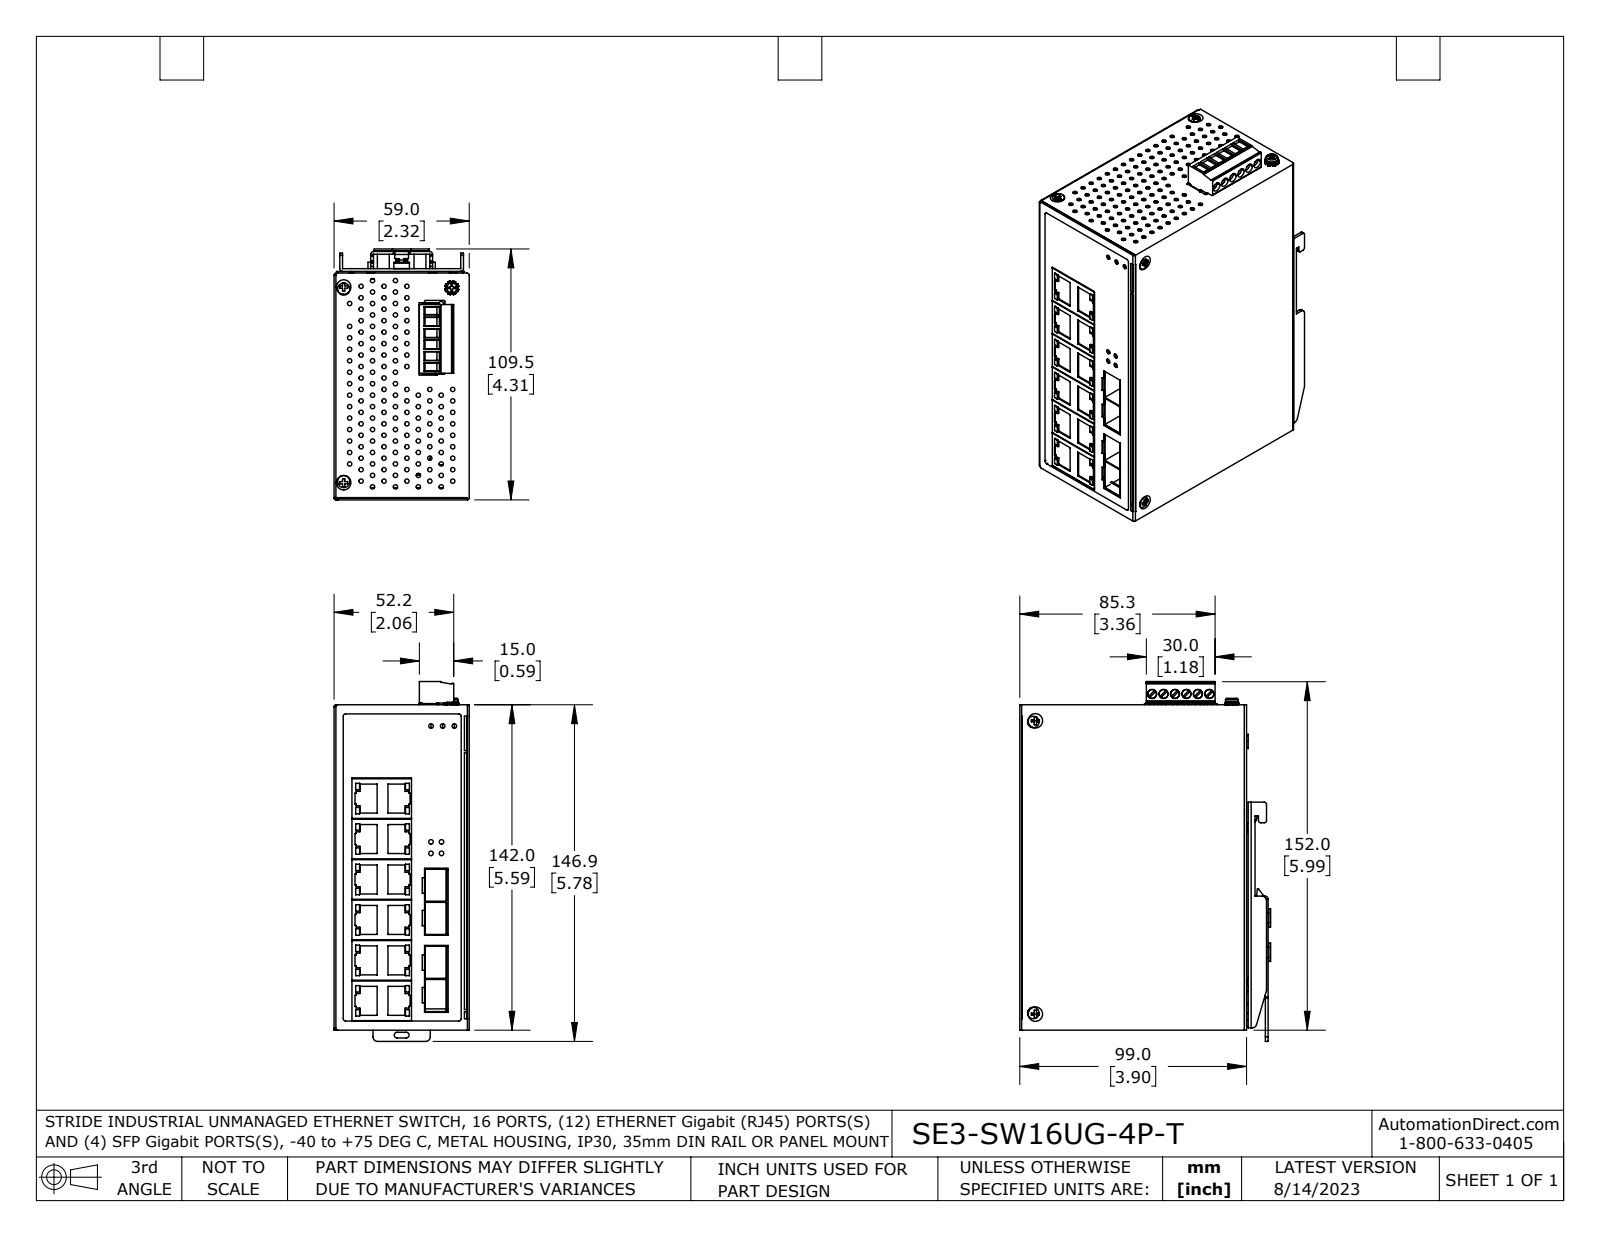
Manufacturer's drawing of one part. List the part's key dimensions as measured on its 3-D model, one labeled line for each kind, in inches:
Part name (STEP PRODUCT): LEONTON_EG2-0800_3D sr1 solid but 16 bad faces1 extTB1ac coord pre CASE MOD for EG2-1604-SFP 59MM CASE ONLY AA mm COMBaCB Modn1B coord fxt fx
STEP written by: SolidWorks 2021 (AUTOMOTIVE_DESIGN)
Units: inches
Bodies: 41 solids, 3056 faces (1495 planar, 1317 cylindrical, 244 other)
Overall size (bounding box): 6.183 × 4.311 × 2.323
Volume: 9.993 in³ · Surface area: 266.2 in²
Round holes (diameter × count): ⌀0.075 ×185, ⌀0.098 ×11, ⌀0.079 ×7, ⌀0.157 ×6, ⌀0.118 ×3, ⌀0.197 ×2, ⌀0.209 ×2
Round bosses / shafts (diameter × count): ⌀0.118 ×32, ⌀0.161 ×8, ⌀0.149 ×6, ⌀0.02 ×6, ⌀0.315 ×3, ⌀0.205 ×3, ⌀0.217 ×1, ⌀0.114 ×1
Partial cylindrical surfaces — rounded edges, fillets, slot ends (radius × count): R0.006 ×72, R0.004 ×63, R0.01 ×32, R0.02 ×18, R0.039 ×16, R0.079 ×15, R0.051 ×12, R0.031 ×8
Main face-to-face distances: 0.031, 0.039, 2.252, 2.291, 2.283, 2.323, 5.559, 0.047, 0.02, 0.37
Hole centre spacings: 0.22, 0.394, 0.599, 0.197, 0.44, 0.787, 0.989, 0.355
